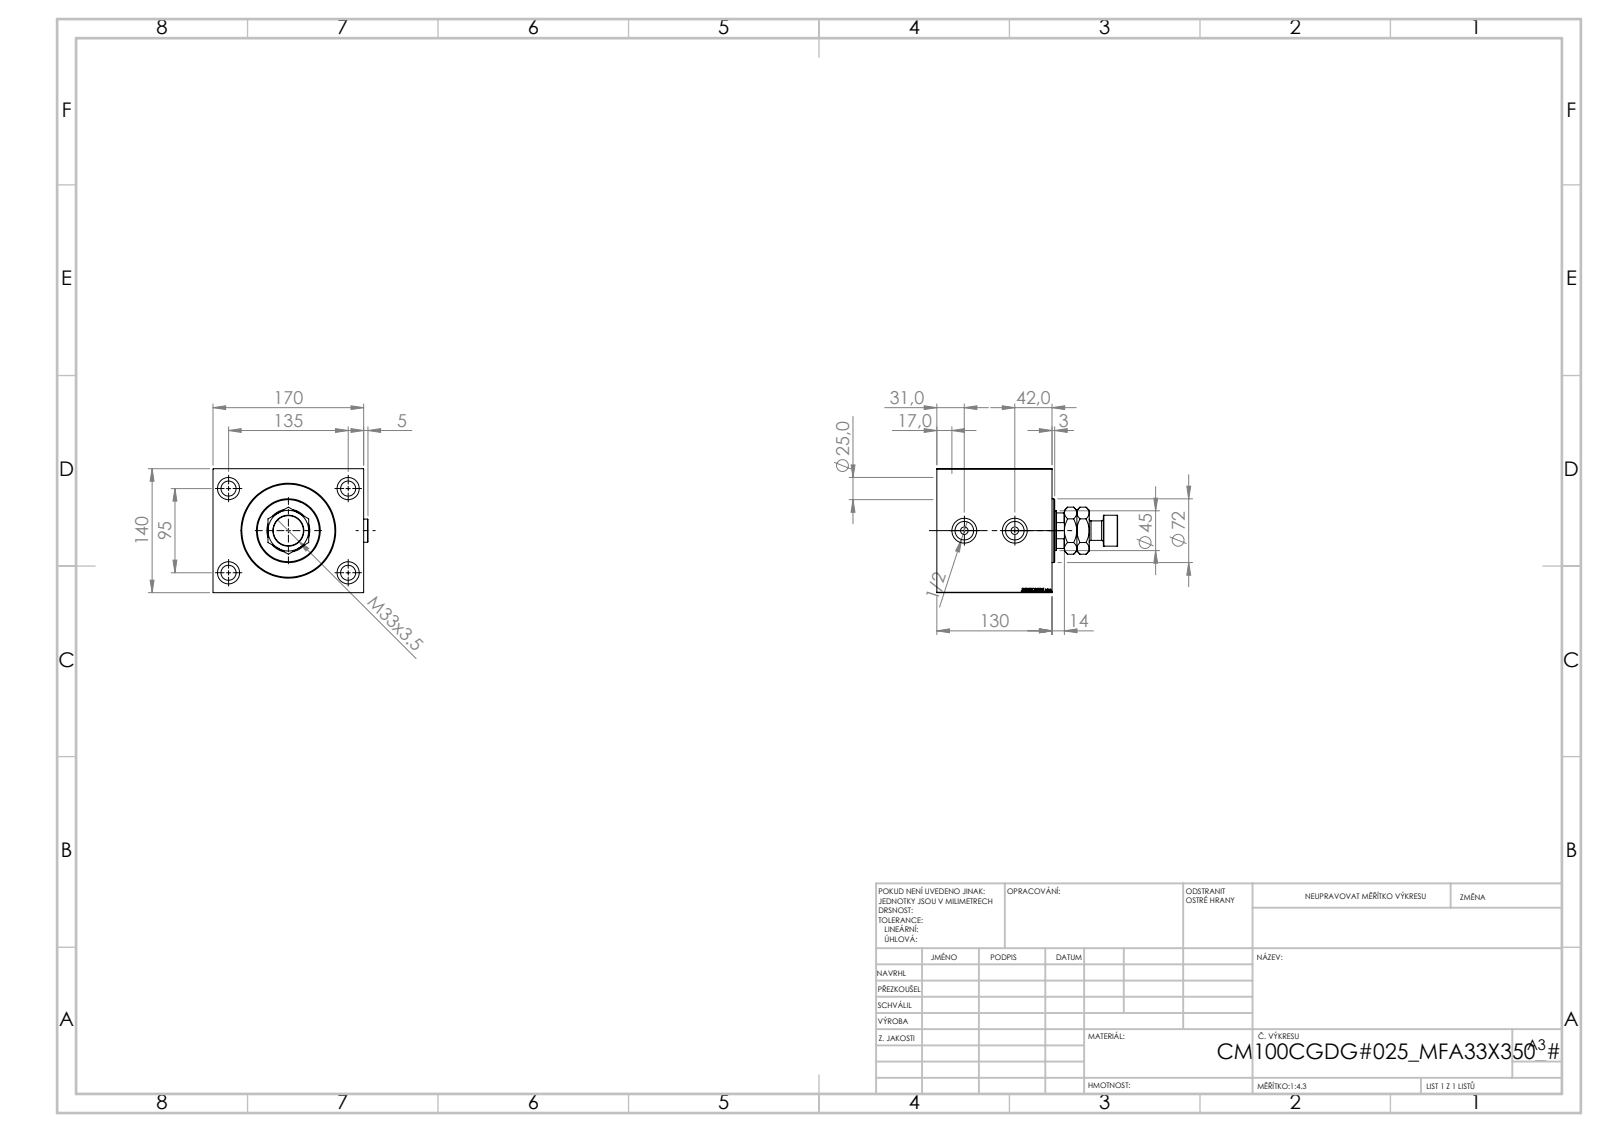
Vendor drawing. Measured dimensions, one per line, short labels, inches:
name: V450CM_C_Body; MFA; Zatka_OIL_PORT; V450CM_C_VCP (+1 more)
written by: SolidWorks 2019 (CONFIG_CONTROL_DESIGN)
unit: in
bodies: 6 solids, 969 faces (459 planar, 80 cylindrical, 430 other)
size: 8.031 × 6.886 × 5.512
volume: 178.3 in³; area: 393.3 in²
holes: 4× ⌀0.669, 4× ⌀0.984, 2× ⌀0.335, 2× ⌀0.825, 2× ⌀1.102, 1× ⌀1.24, 1× ⌀1.772, 1× ⌀1.909, 1× ⌀3.937, 1× ⌀4.016, 1× ⌀4.134
bosses: 2× ⌀1.024, 1× ⌀2.835, 1× ⌀1.378, 1× ⌀0.866
rounds: 1× R0.866
face distances: 5.512, 5.118, 6.693, 3.11, 2.008, 0.85, 1.157, 4.268, 0.394, 1.244
hole spacings: 3.25, 3.74, 5.315, 6.499, 2.244
